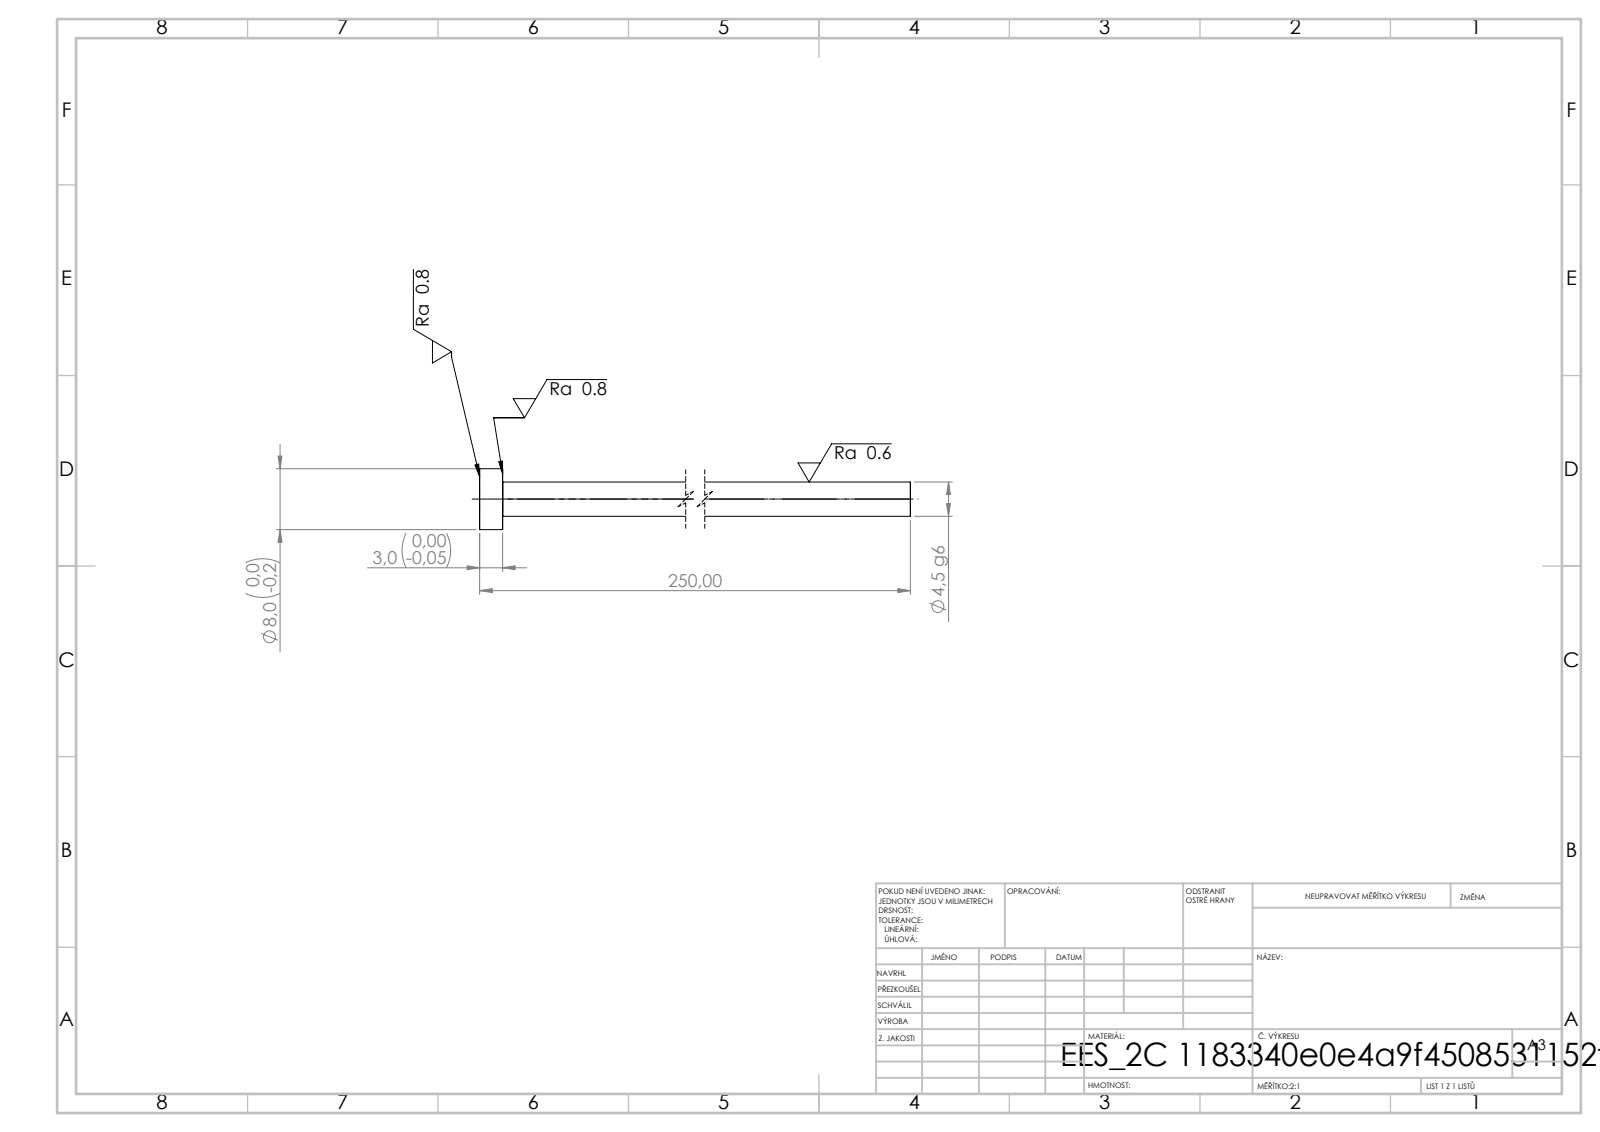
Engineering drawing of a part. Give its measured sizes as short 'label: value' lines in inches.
written by: SolidWorks 2019 (CONFIG_CONTROL_DESIGN)
unit: in
bodies: 1 solid, 7 faces (3 planar, 4 cylindrical, 0 other)
size: 9.843 × 0.315 × 0.315
volume: 0.249 in³; area: 5.685 in²
bosses: 1× ⌀0.315, 1× ⌀0.177
face distances: 0.118, 9.843, 9.724
